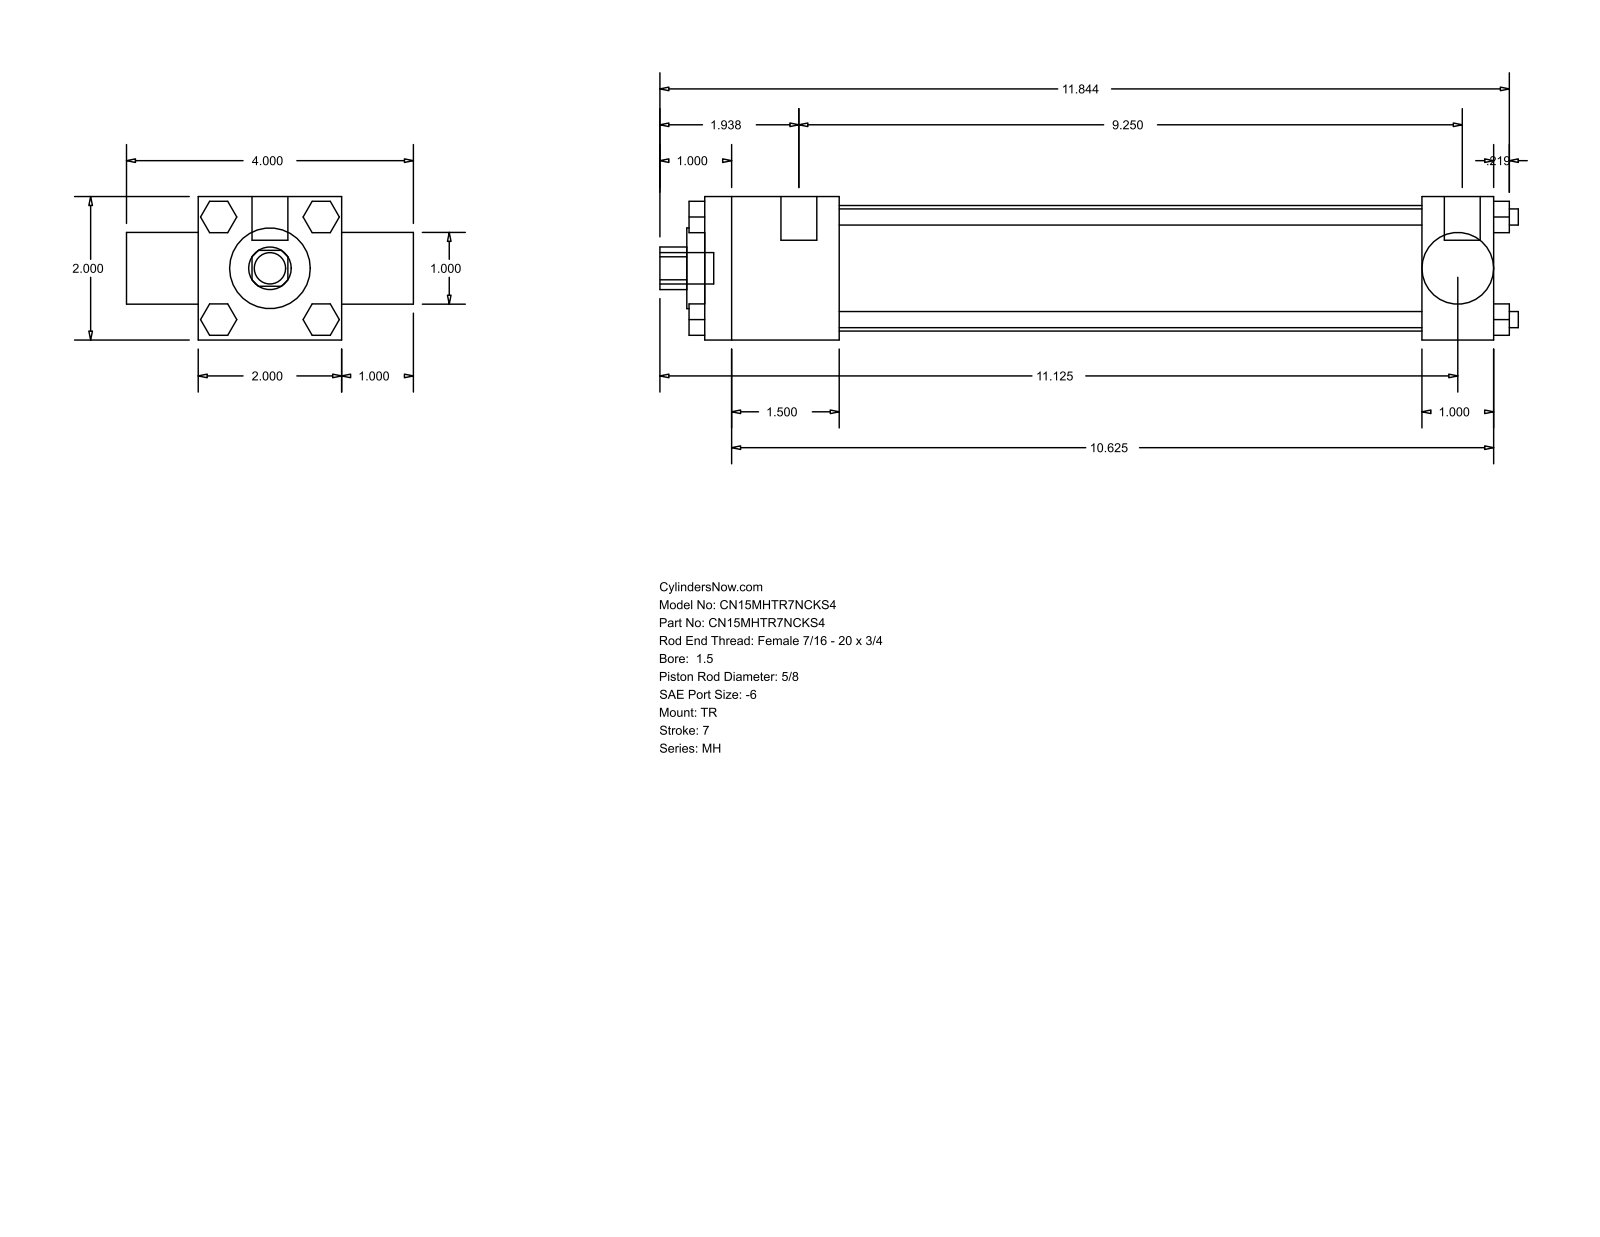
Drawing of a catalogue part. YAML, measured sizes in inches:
part_name: "MH_TR__0150_0.625"
step_written_by: "GSSL Pune (CONFIG_CONTROL_DESIGN)"
units: inches
bodies: {solids: 0, faces: 120, planar: 92, cylindrical: 28, other: 0}
overall_size: [11.969, 4, 2]
round_holes:
  - {diameter: 0.625, count: 1}
  - {diameter: 0.998, count: 1}
  - {diameter: 1.125, count: 1}
  - {diameter: 1.75, count: 1}
round_bosses_or_shafts:
  - {diameter: 0.225, count: 4}
  - {diameter: 0.219, count: 3}
  - {diameter: 0.5, count: 2}
  - {diameter: 0.437, count: 1}
partial_cylinders:
  - {radius: 0.297, count: 1}
face_to_face_distances: [2, 11, 1, 3, 1.875, 9.125, 10, 8.125, 1, 0.219]
